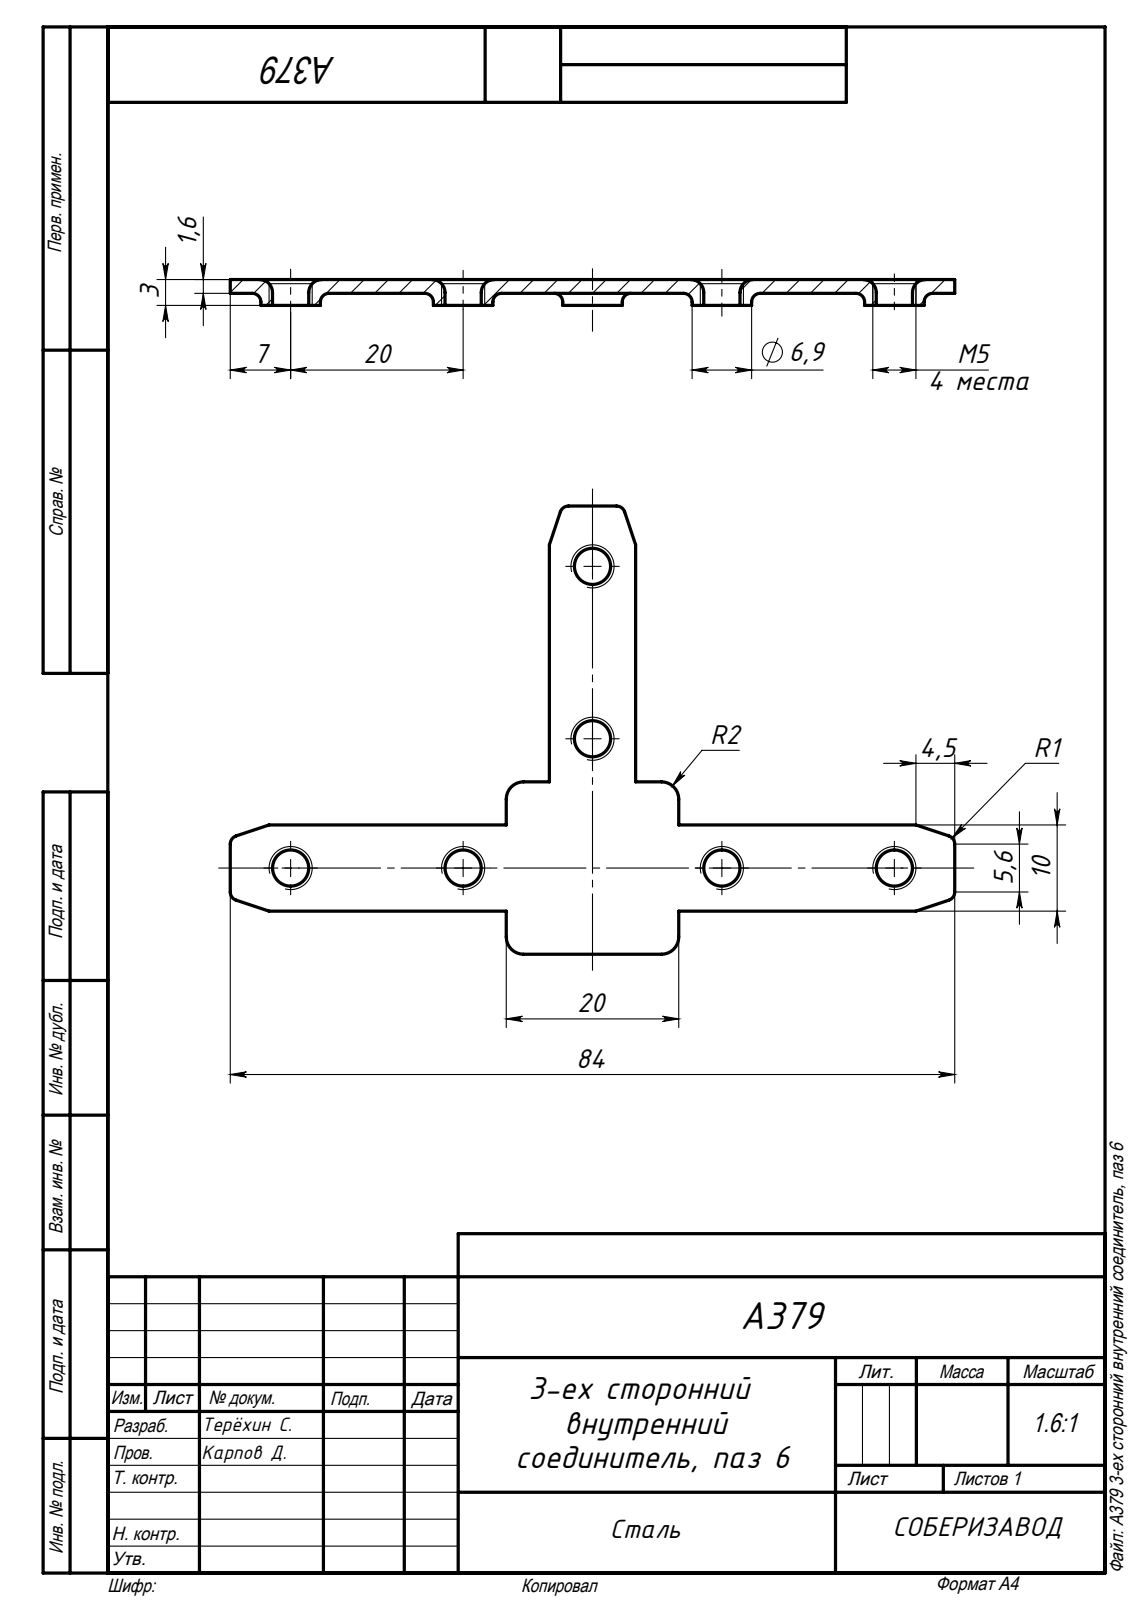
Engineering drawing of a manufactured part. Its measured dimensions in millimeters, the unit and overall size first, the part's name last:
Units: millimetres
Overall size (bounding box): 84 × 52 × 3
Round holes (diameter × count): ⌀4.2 ×6
Round bosses / shafts (diameter × count): ⌀6.9 ×6
Partial cylindrical surfaces — rounded edges, fillets, slot ends (radius × count): R1 ×6, R2 ×4
Main face-to-face distances: 1.6, 1.4, 3, 10, 5, 15, 32, 37, 47, 52
Hole centre spacings: 38.08, 20, 21.21, 49.5, 50, 30, 70
Volume: 2 187 mm³ · Surface area: 3 242 mm²
Bodies: 1 solid, 88 faces (30 planar, 34 cylindrical, 24 other)
Part name (STEP PRODUCT): A379 3-ех сторонний внутренний соединитель, паз 6
STEP written by: SolidWorks 2020 (AUTOMOTIVE_DESIGN)
